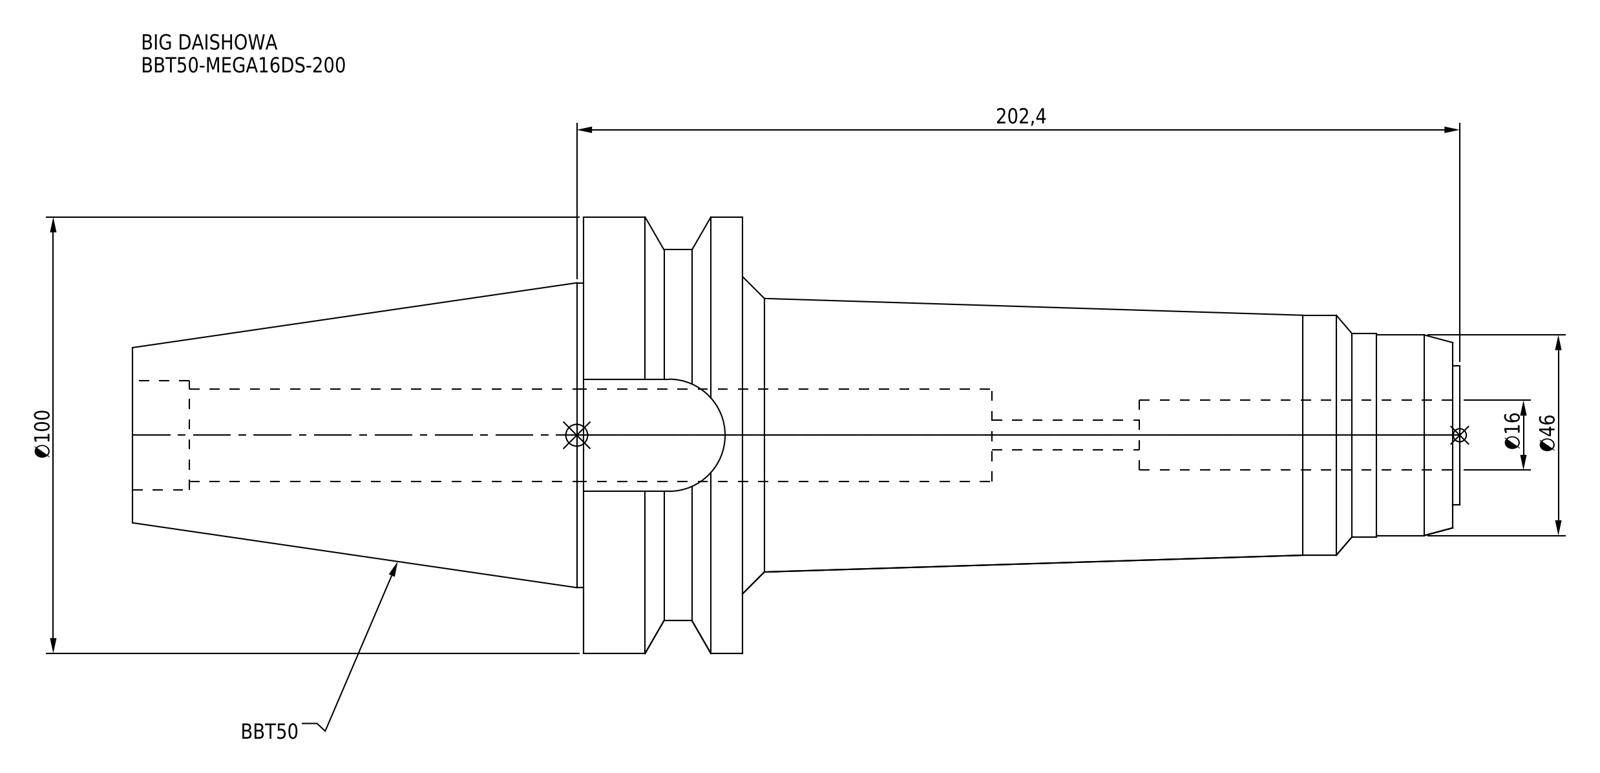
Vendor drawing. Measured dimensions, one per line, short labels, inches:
name: BBT50-MEGA16DS-200
written by: CREO PARAMETRIC BY PTC INC, 2016380 (AUTOMOTIVE_DESIGN)
unit: in
bodies: 1 solid, 57 faces (15 planar, 28 cylindrical, 14 other)
size: 11.976 × 3.937 × 3.937
volume: 50.68 in³; area: 140 in²
holes: 1× ⌀0.268, 1× ⌀0.63, 1× ⌀0.835, 1× ⌀0.984
bosses: 1× ⌀3.937, 1× ⌀3.346, 1× ⌀2.75, 1× ⌀2.165, 1× ⌀1.839, 1× ⌀1.811, 1× ⌀1.256
rounds: 1× R0.506
face distances: 1.437, 5.504, 4.067, 2.787, 6.409, 7.846, 11.913, 0.063, 6.472, 7.909
